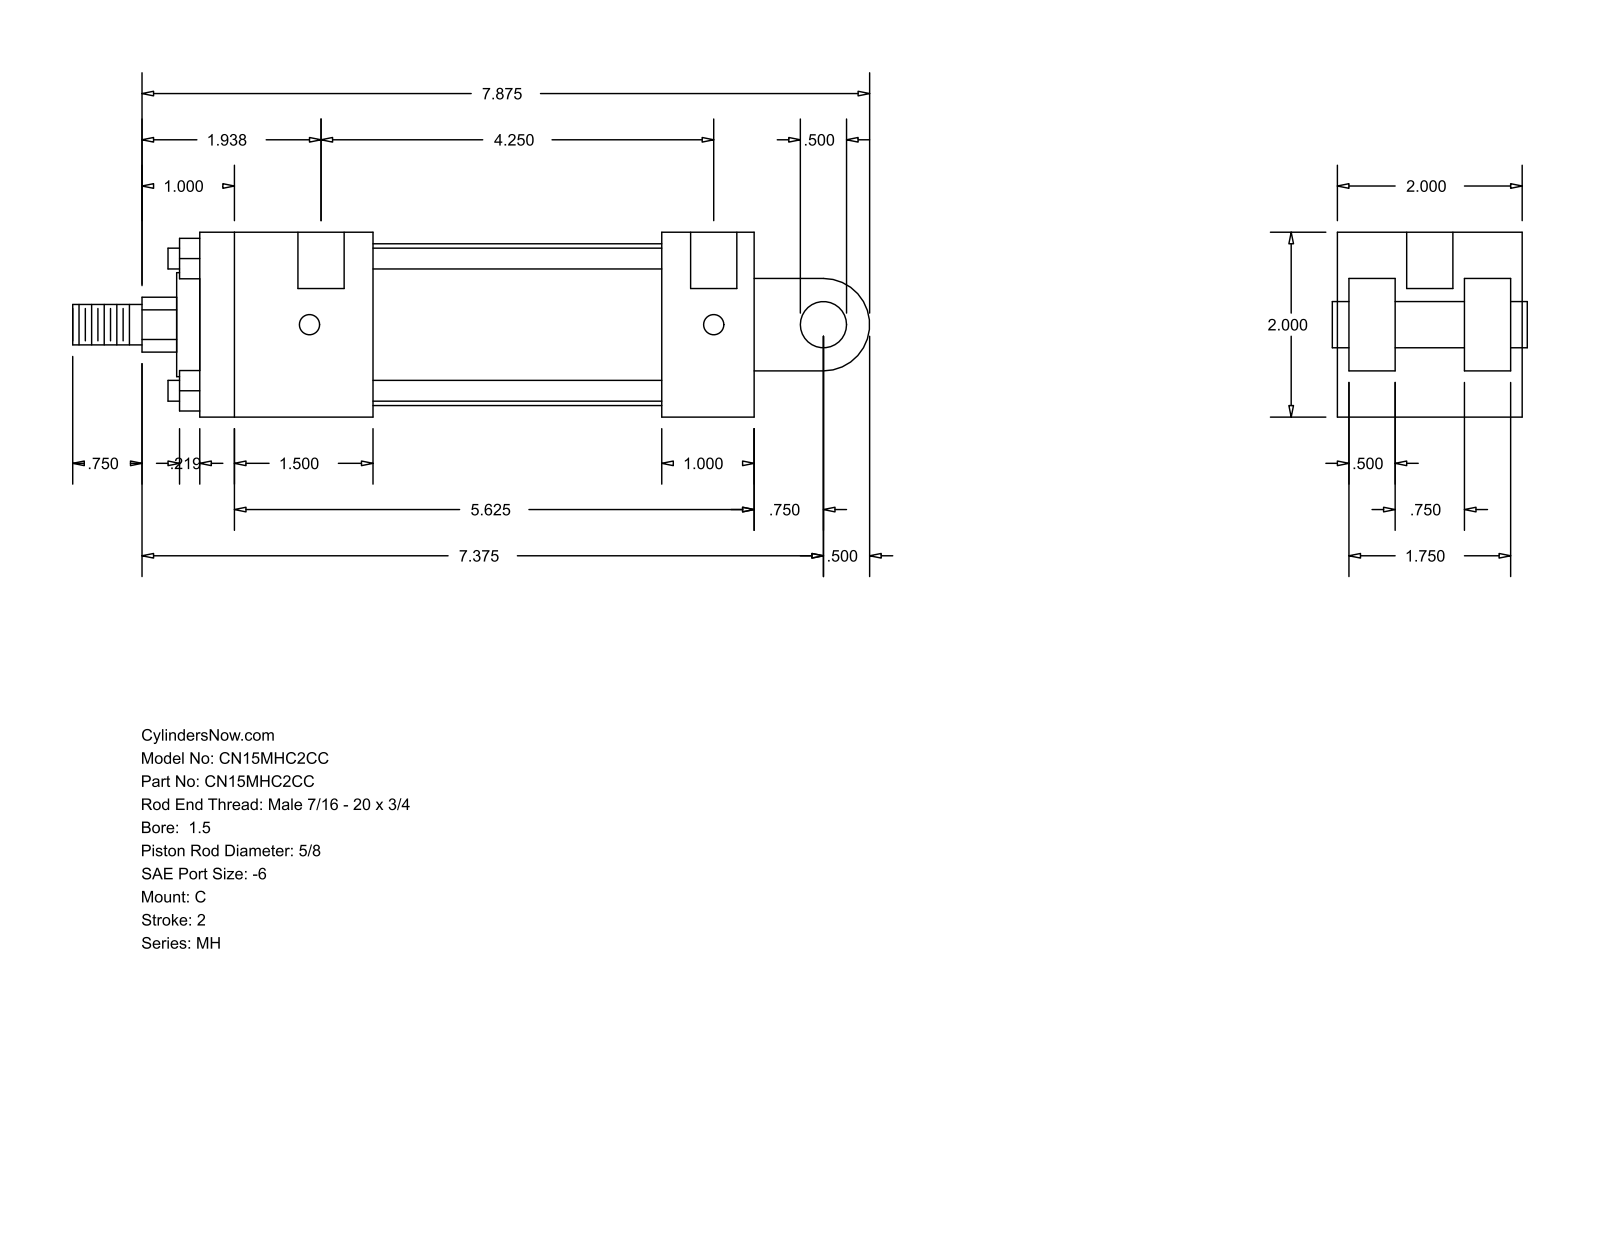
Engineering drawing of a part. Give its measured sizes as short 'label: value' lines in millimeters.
name: MH_C__0150_0.625
written by: GSSL Pune (CONFIG_CONTROL_DESIGN)
unit: mm
bodies: 0 solids, 99 faces (70 planar, 29 cylindrical, 0 other)
size: 219.07 × 50.8 × 50.8
holes: 4× ⌀5.56, 2× ⌀12.7
bosses: 4× ⌀5.71, 1× ⌀44.45, 1× ⌀28.57, 1× ⌀15.88, 1× ⌀12.7, 1× ⌀11.11
rounds: 1× R7.54, 1× R12.7
face distances: 50.8, 12.7, 152.4, 25.4, 34.93, 3.17, 47.63, 15.87, 31.76, 38.1
hole spacings: 111.12, 3.17, 107.95
